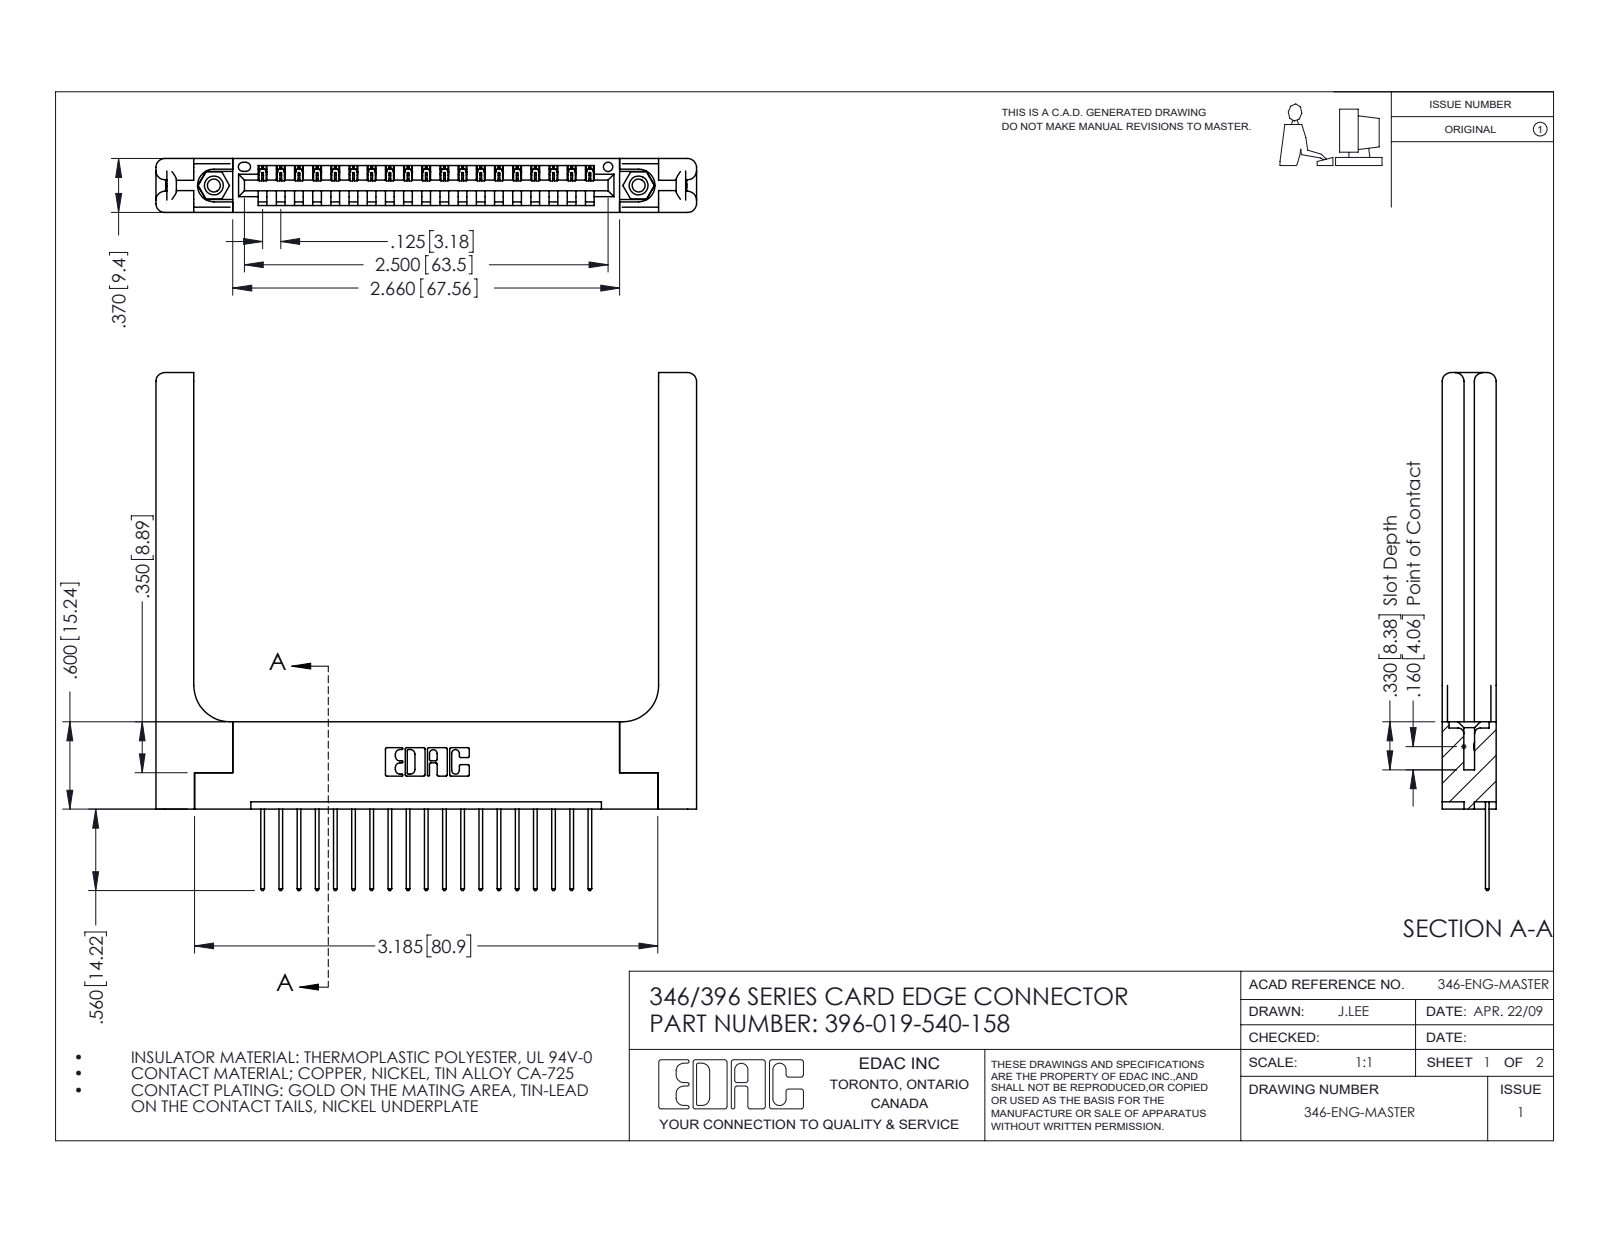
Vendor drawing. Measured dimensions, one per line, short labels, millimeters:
name: 345-250-001_345-250-001-102; 346-220-058_345-220-058; 345-292-001_345-293-140; 346 Part_Flush Mounting Lugs - 0.156 Dia-TH (+1 more)
written by: SolidWorks 2016 (CONFIG_CONTROL_DESIGN)
unit: mm
bodies: 24 solids, 1480 faces (984 planar, 436 cylindrical, 60 other)
size: 94.4 × 90.4 × 9.4
volume: 16 420 mm³; area: 16 240 mm²
holes: 2× ⌀2.3, 2× ⌀3.2, 2× ⌀4, 1× ⌀1.6
bosses: 2× ⌀3.9
rounds: 38× R0.2, 38× R0.3, 22× R0.3, 16× R1.5, 6× R0.2, 6× R0.8, 3× R0.7, 2× R0.8
face distances: 9.4, 1.8, 3.8, 1.2, 8.2, 3.8, 6.4, 7.6, 0.6, 2.6
hole spacings: 6.2, 68.9, 74.2
